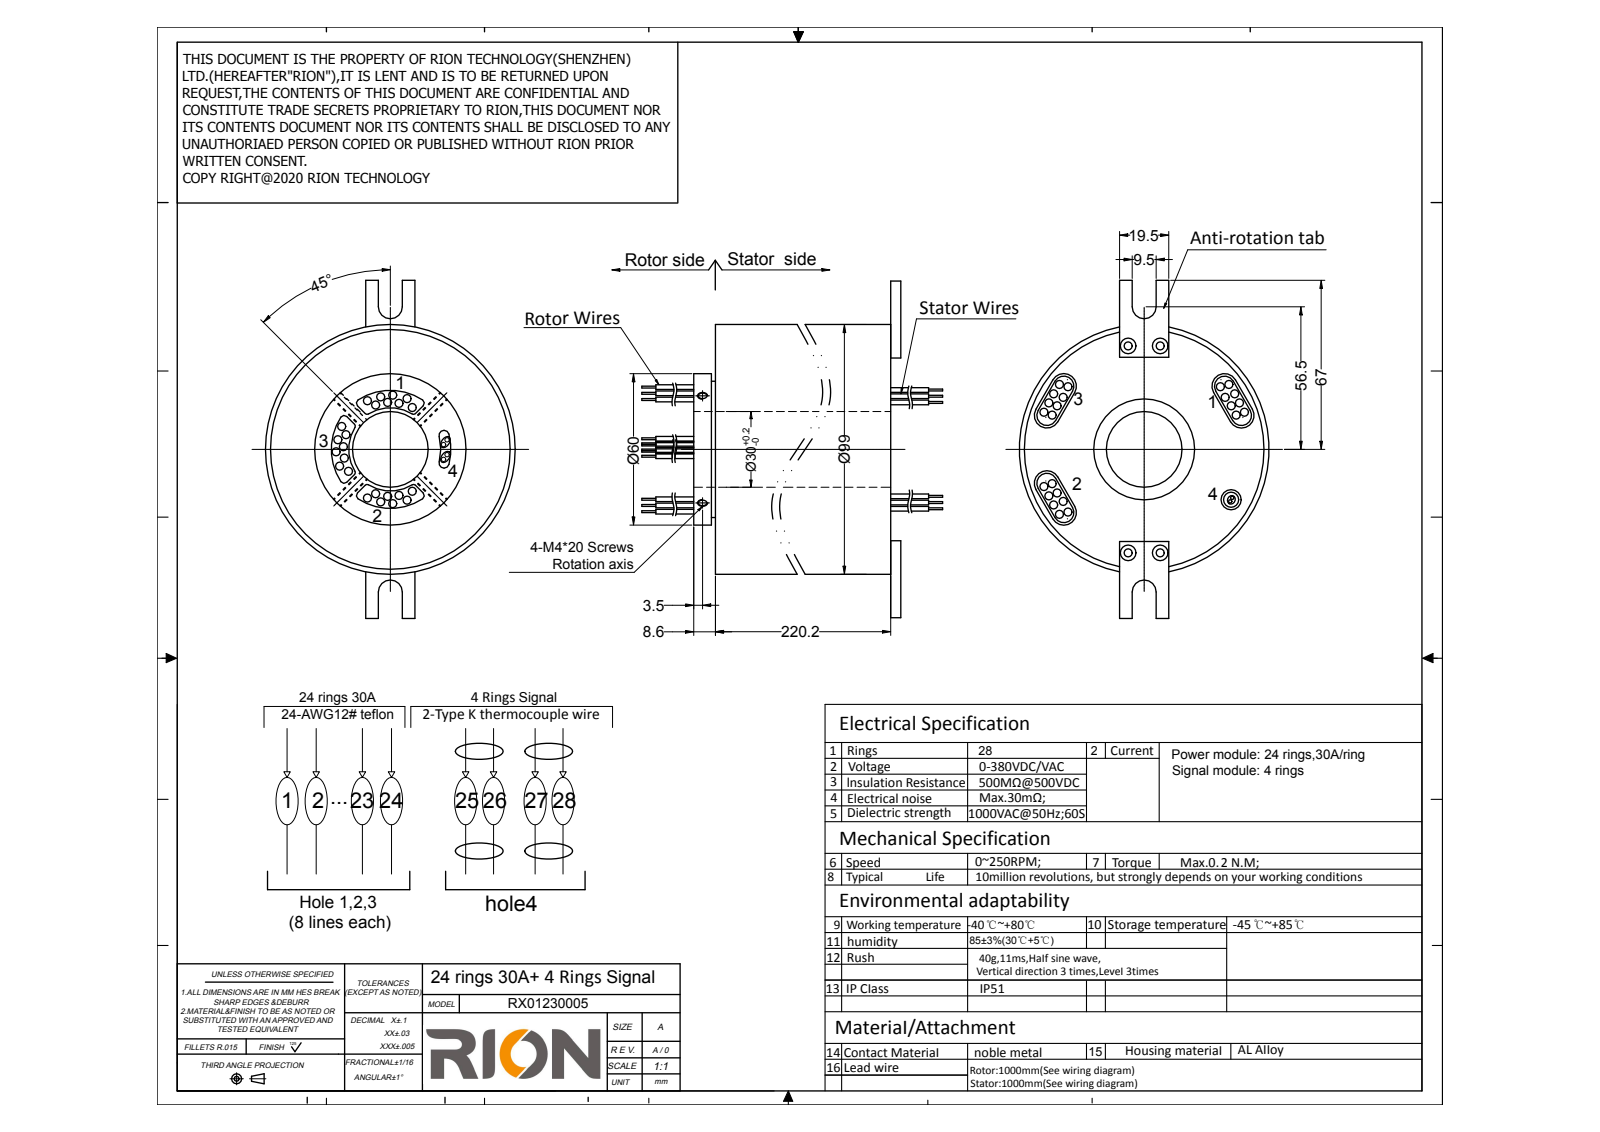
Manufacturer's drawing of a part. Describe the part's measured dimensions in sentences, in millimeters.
Its 3-D file was written by "SolidWorks 2014 (CONFIG_CONTROL_DESIGN)". It is 1 solid with 313 faces: 106 planar, 186 cylindrical and 21 other. Overall it measures 268.8 by 134 by 99 millimeters. Its volume is 1 567 000 cubic millimeters and its surface area 127 280 square millimeters. Round holes: 4 of diameter 2.5, 4 of diameter 3.2, 4 of diameter 3.3, 1 of diameter 8, 1 of diameter 30, 1 of diameter 40, 1 of diameter 95. Round bosses or shafts: 48 of diameter 3.2, 1 of diameter 99, 1 of diameter 94.8, 1 of diameter 60, 1 of diameter 54, 1 of diameter 39.8, 1 of diameter 6. Partial cylindrical surfaces (rounded edges, fillets, slot ends): 6 of radius 1, 6 of radius 1.5, 6 of radius 4, 2 of radius 2, 2 of radius 4.75, 1 of radius 1.2, 1 of radius 16.5, 1 of radius 20. The main face-to-face distances are 220.2, 8.6, 228.8, 4, 232.8, 224.2, 1, 227.8, 7, 1.6. The hole center spacings are 41.49, 12.7, 82, 82.98, 35.13, 39.83, 45.93, 67.12.
